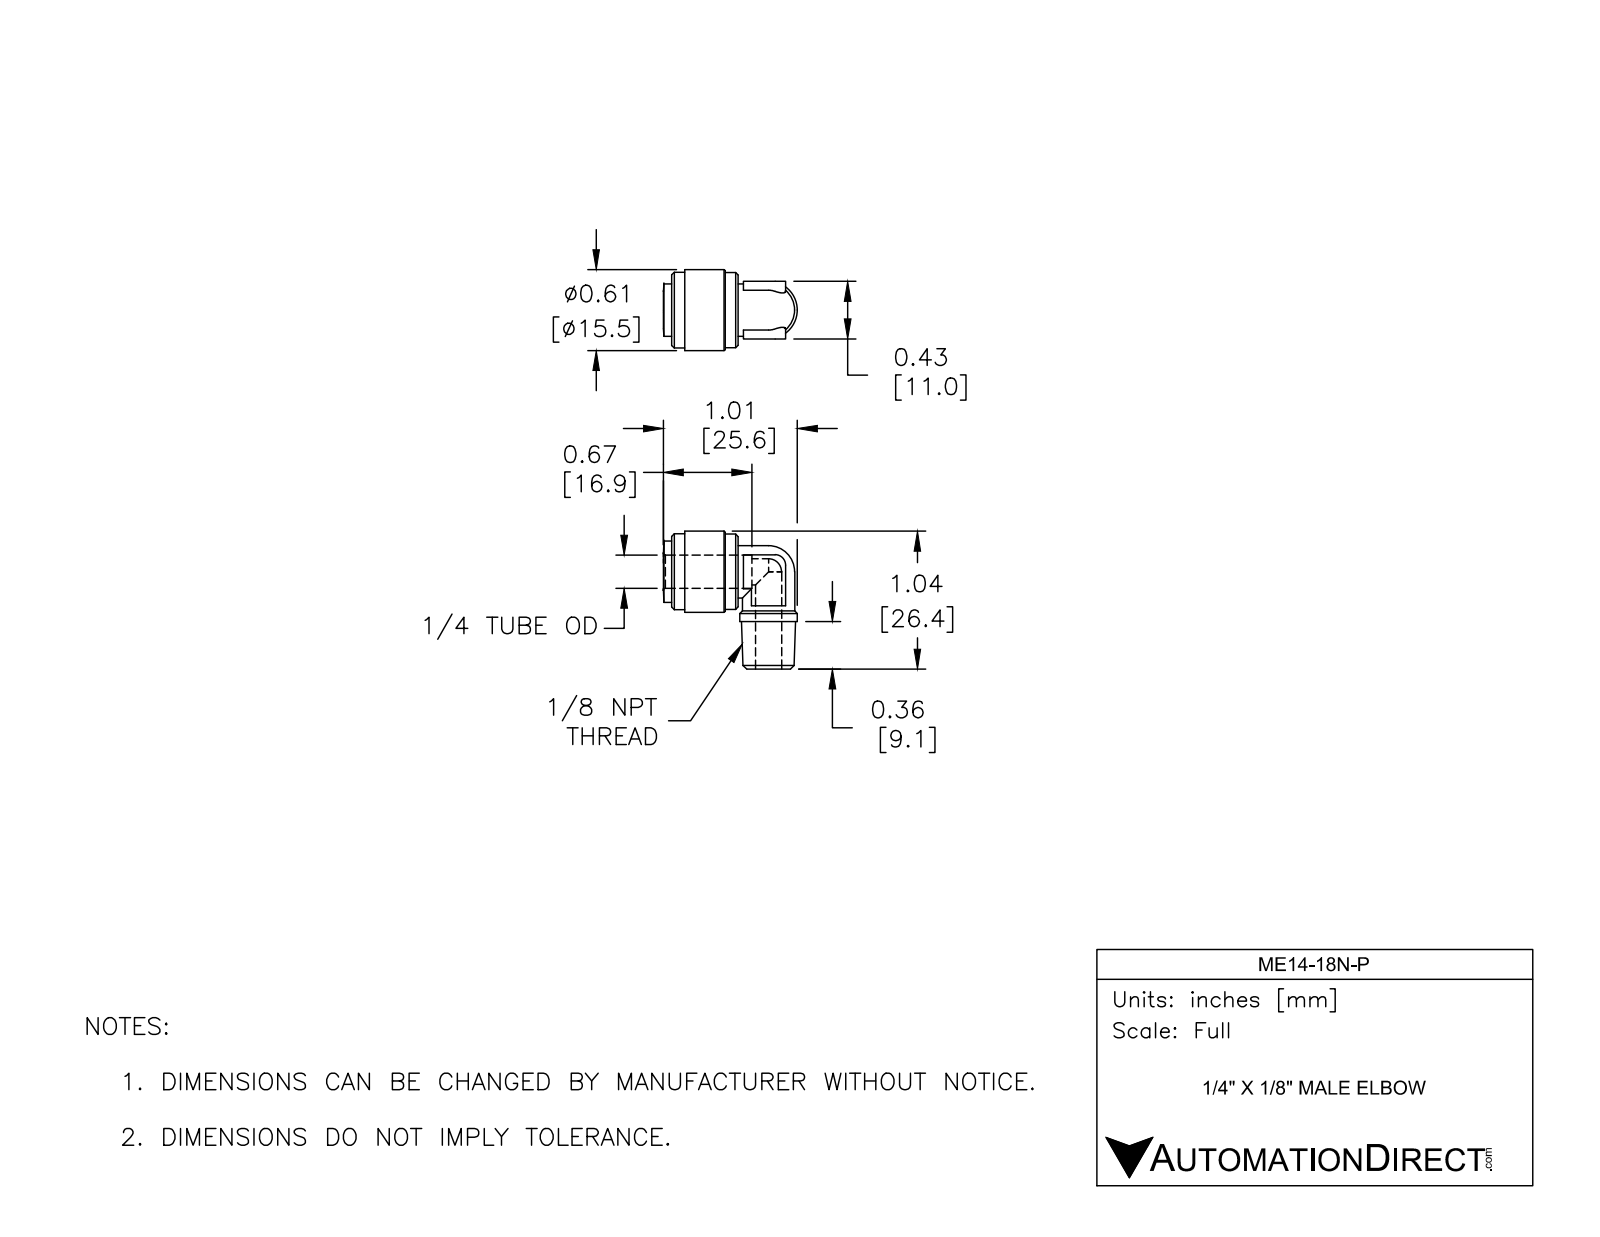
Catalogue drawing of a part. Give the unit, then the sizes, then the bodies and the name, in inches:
Units: inches
Overall size (bounding box): 1.037 × 1.008 × 0.61
Round holes (diameter × count): ⌀0.197 ×2, ⌀0.25 ×1
Round bosses / shafts (diameter × count): ⌀0.394 ×2, ⌀0.61 ×1, ⌀0.571 ×1, ⌀0.567 ×1, ⌀0.433 ×1
Partial cylindrical surfaces — rounded edges, fillets, slot ends (radius × count): R0.079 ×1
Main face-to-face distances: 0.433, 0.5, 0.098, 0.402, 0.856, 0.356, 0.758, 0.502, 0.86, 0.256
Volume: 0.212 in³ · Surface area: 3.824 in²
Bodies: 1 solid, 63 faces (21 planar, 20 cylindrical, 22 other)
Part name (STEP PRODUCT): ME14-18N-P
STEP written by: SolidWorks 2017 (AUTOMOTIVE_DESIGN)
